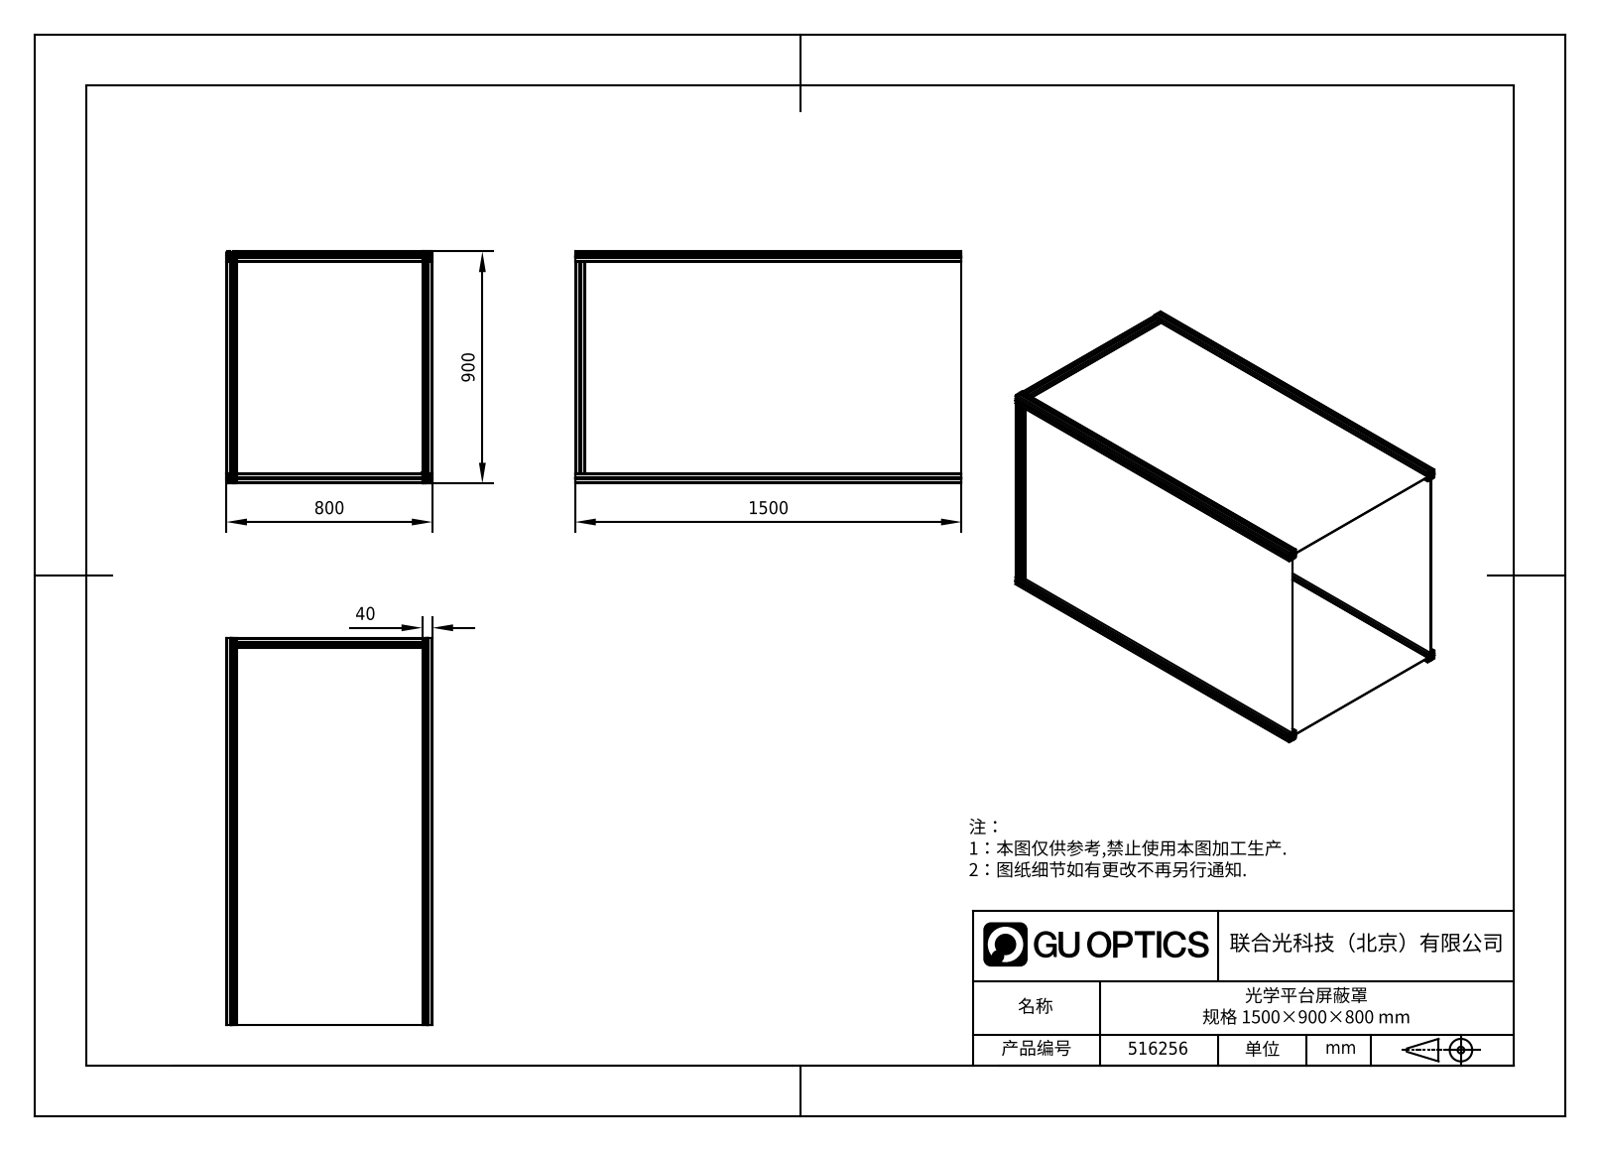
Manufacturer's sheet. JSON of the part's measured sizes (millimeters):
{"part_name": "光学平台屏蔽罩边框_820; 光学平台屏蔽罩面板_744_1472; 光学平台屏蔽罩面板_744_844; 光学平台屏蔽罩边框_720 (+3 more)", "step_written_by": "SolidWorks 2020 (CONFIG_CONTROL_DESIGN)", "units": "millimeters", "bodies": {"solids": 13, "faces": 1230, "planar": 950, "cylindrical": 280, "other": 0}, "overall_size": [1500, 900, 800], "volume_mm3": 16050000, "surface_area_mm2": 15130000, "partial_cylinders_radius": [[0.5, 64], [1, 64], [0.75, 32], [2.5, 32], [4.5, 32], [3.4, 8]], "face_to_face_distances": [2, 760, 860, 762, 758, 862, 858, 19, 21, 8.2]}
